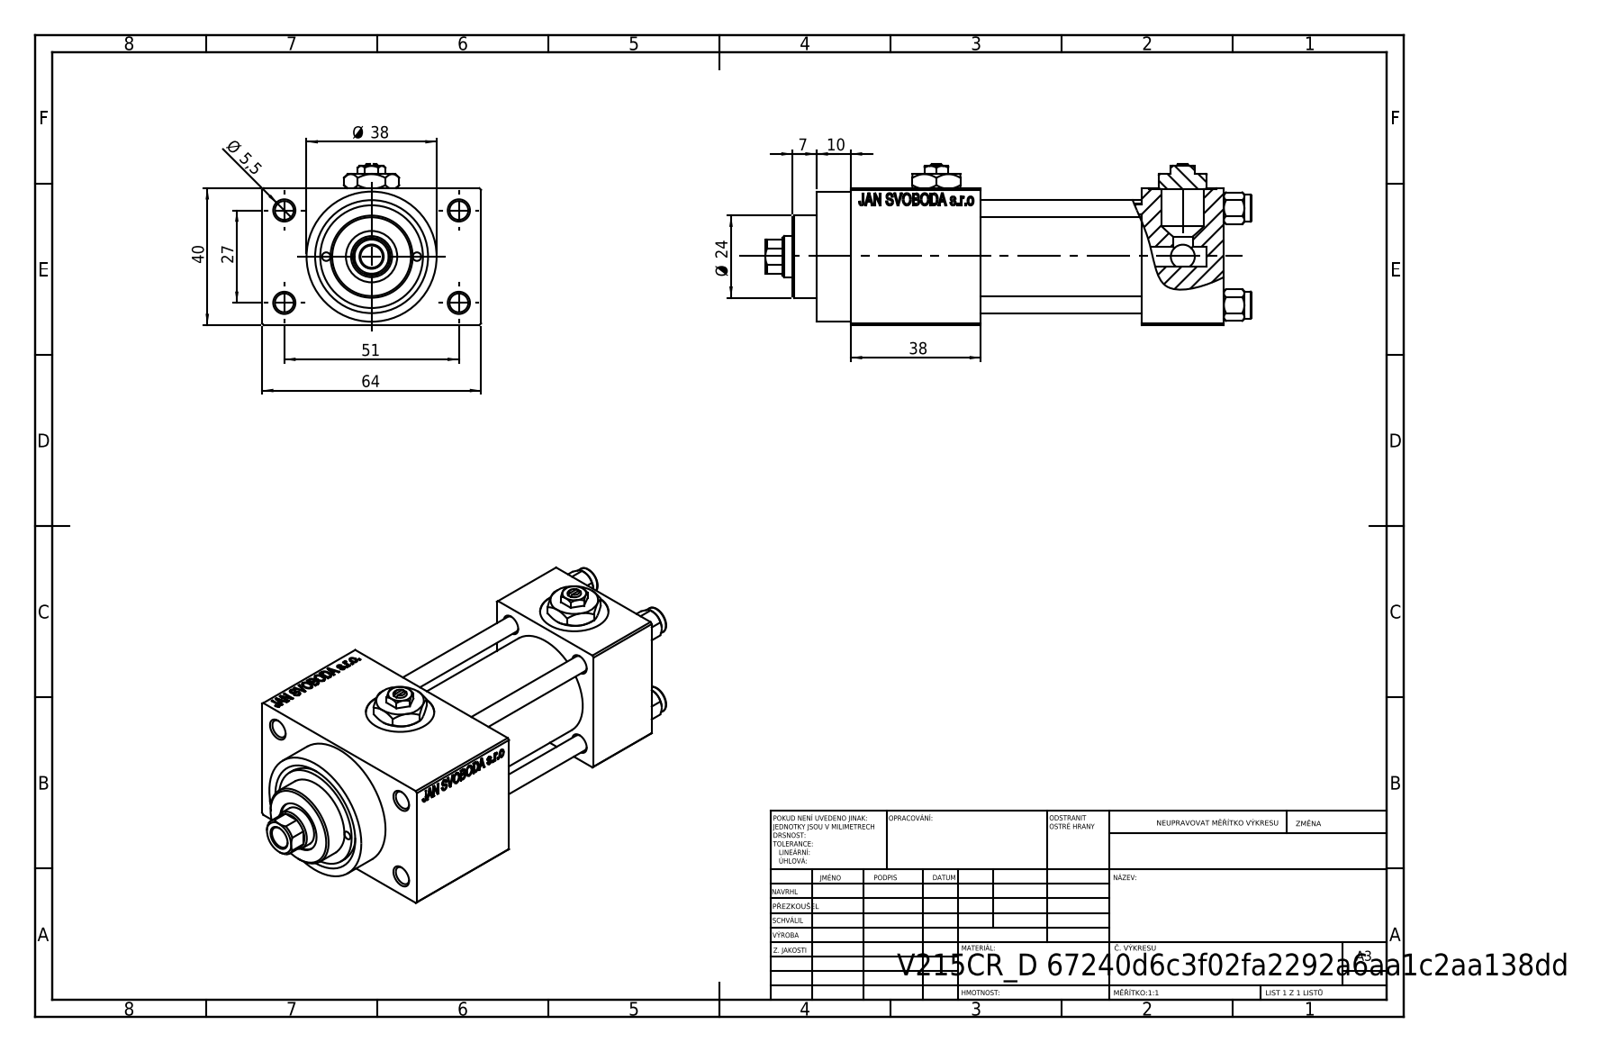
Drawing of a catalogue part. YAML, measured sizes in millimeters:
part_name: "V215CR_VCP_D; V215_VC_A; NUT_M5_D; V215CR_D_Body (+2 more)"
step_written_by: "SolidWorks 2019 (CONFIG_CONTROL_DESIGN)"
units: millimeters
bodies: {solids: 13, faces: 1209, planar: 544, cylindrical: 103, other: 562}
overall_size: [142, 64, 47]
volume: 172500
surface_area: 63805
round_holes:
  - {diameter: 20, count: 5}
  - {diameter: 5, count: 4}
  - {diameter: 5.5, count: 4}
  - {diameter: 13.16, count: 4}
  - {diameter: 7, count: 3}
  - {diameter: 2.5, count: 2}
  - {diameter: 6.5, count: 1}
  - {diameter: 12, count: 1}
  - {diameter: 15, count: 1}
  - {diameter: 25, count: 1}
  - {diameter: 30, count: 1}
round_bosses_or_shafts:
  - {diameter: 8, count: 4}
  - {diameter: 38, count: 1}
  - {diameter: 31, count: 1}
  - {diameter: 24, count: 1}
partial_cylinders:
  - {radius: 5.5, count: 1}
face_to_face_distances: [40, 12, 47, 52, 24, 71, 38, 85, 109, 64]
hole_center_spacings: [11.37, 14.18, 18.23, 20.01, 28.3, 28.85, 29.89, 30.84]
